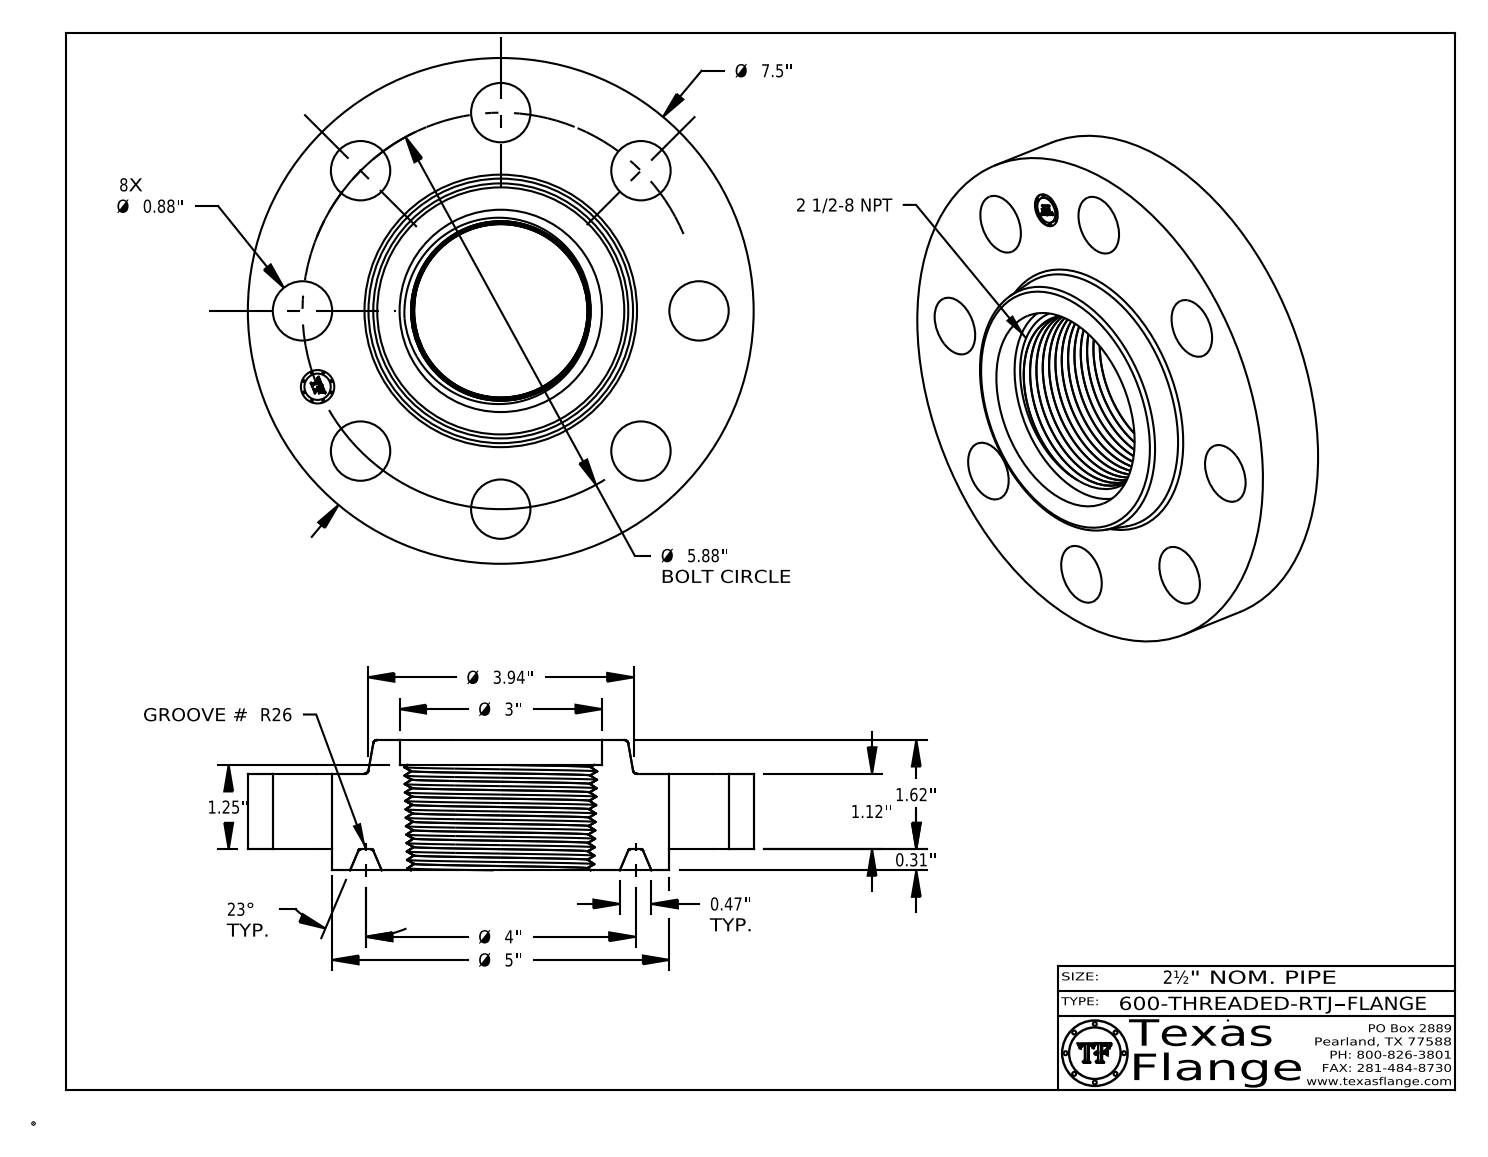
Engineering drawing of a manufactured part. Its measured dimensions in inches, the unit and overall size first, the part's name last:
Units: inches
Overall size (bounding box): 7.5 × 7.5 × 1.933
Round holes (diameter × count): ⌀0.88 ×8, ⌀0.495 ×1, ⌀3 ×1
Round bosses / shafts (diameter × count): ⌀0.03 ×8, ⌀7.5 ×1, ⌀5 ×1, ⌀0.39 ×1
Main face-to-face distances: 1.12, 0.313, 1.433, 1.933, 1.62, 0.5, 1.563, 1.25, 0.13, 0.37
Hole centre spacings: 2.25, 5.432, 2.94, 2.94, 4.157, 4.158, 3.267, 5.88
Volume: 43.02 in³ · Surface area: 161.4 in²
Bodies: 1 solid, 560 faces (372 planar, 42 cylindrical, 146 other)
Part name (STEP PRODUCT): 600-THREADED-RTJ
STEP written by: CATIA V5 STEP AP214 (AUTOMOTIVE_DESIGN)
